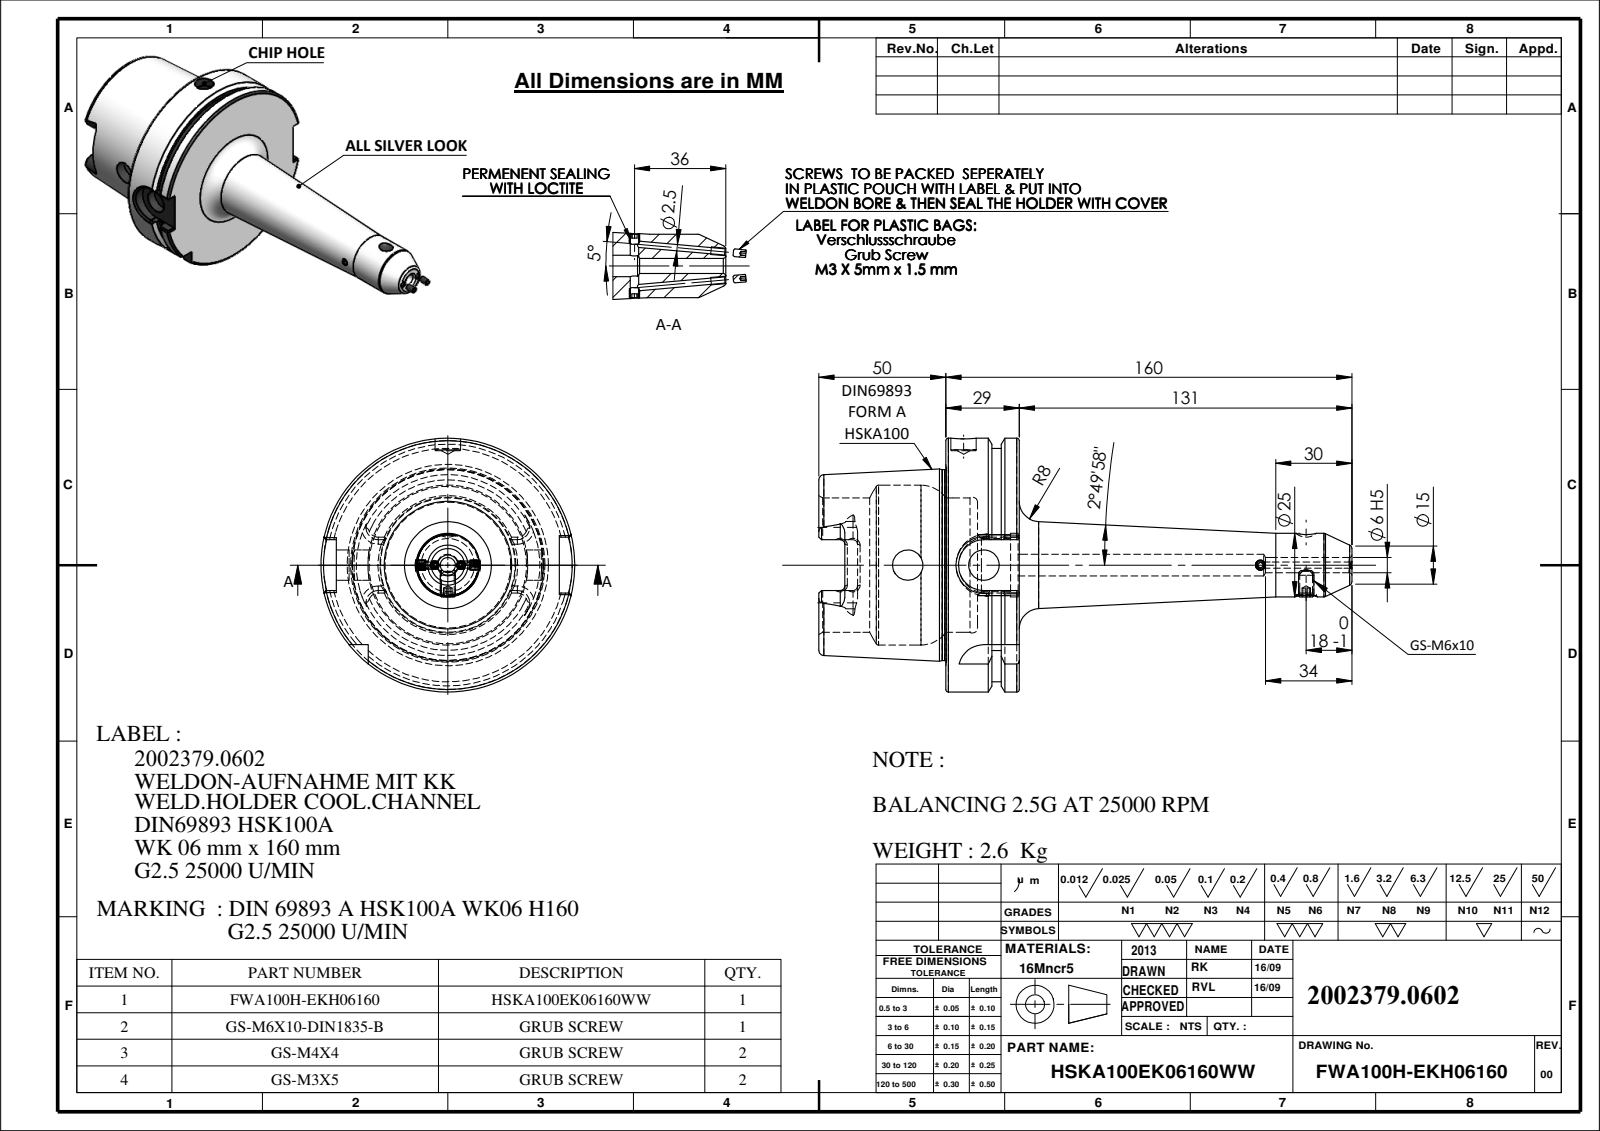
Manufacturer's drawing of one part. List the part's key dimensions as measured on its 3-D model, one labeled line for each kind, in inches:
Part name (STEP PRODUCT): 91100A-WK06160; GS-M4X4_DIN 913 - M4 x 4-N; GS-M3X5; HSKA100EK06160WW (+1 more)
STEP written by: SolidWorks 2018 (CONFIG_CONTROL_DESIGN)
Units: inches
Bodies: 6 solids, 358 faces (110 planar, 88 cylindrical, 160 other)
Overall size (bounding box): 8.583 × 3.937 × 3.937
Volume: 20.34 in³ · Surface area: 100.9 in²
Round holes (diameter × count): ⌀0.098 ×2, ⌀0.472 ×2, ⌀0.13 ×1, ⌀0.197 ×1, ⌀0.236 ×1, ⌀0.315 ×1, ⌀0.335 ×1, ⌀0.394 ×1, ⌀0.827 ×1, ⌀0.984 ×1, ⌀2.087 ×1, ⌀2.48 ×1
Round bosses / shafts (diameter × count): ⌀0.118 ×2, ⌀3.937 ×1, ⌀3.622 ×1, ⌀2.959 ×1, ⌀0.236 ×1, ⌀0.157 ×1
Partial cylindrical surfaces — rounded edges, fillets, slot ends (radius × count): R0.071 ×6, R0.192 ×4, R0.394 ×2, R0.433 ×1
Main face-to-face distances: 1.14, 0.492, 0.648, 1.969, 2.461, 3.108, 3.091, 1.122, 0.63, 0.018
Hole centre spacings: 1.181, 4.291, 5.315, 5.472
